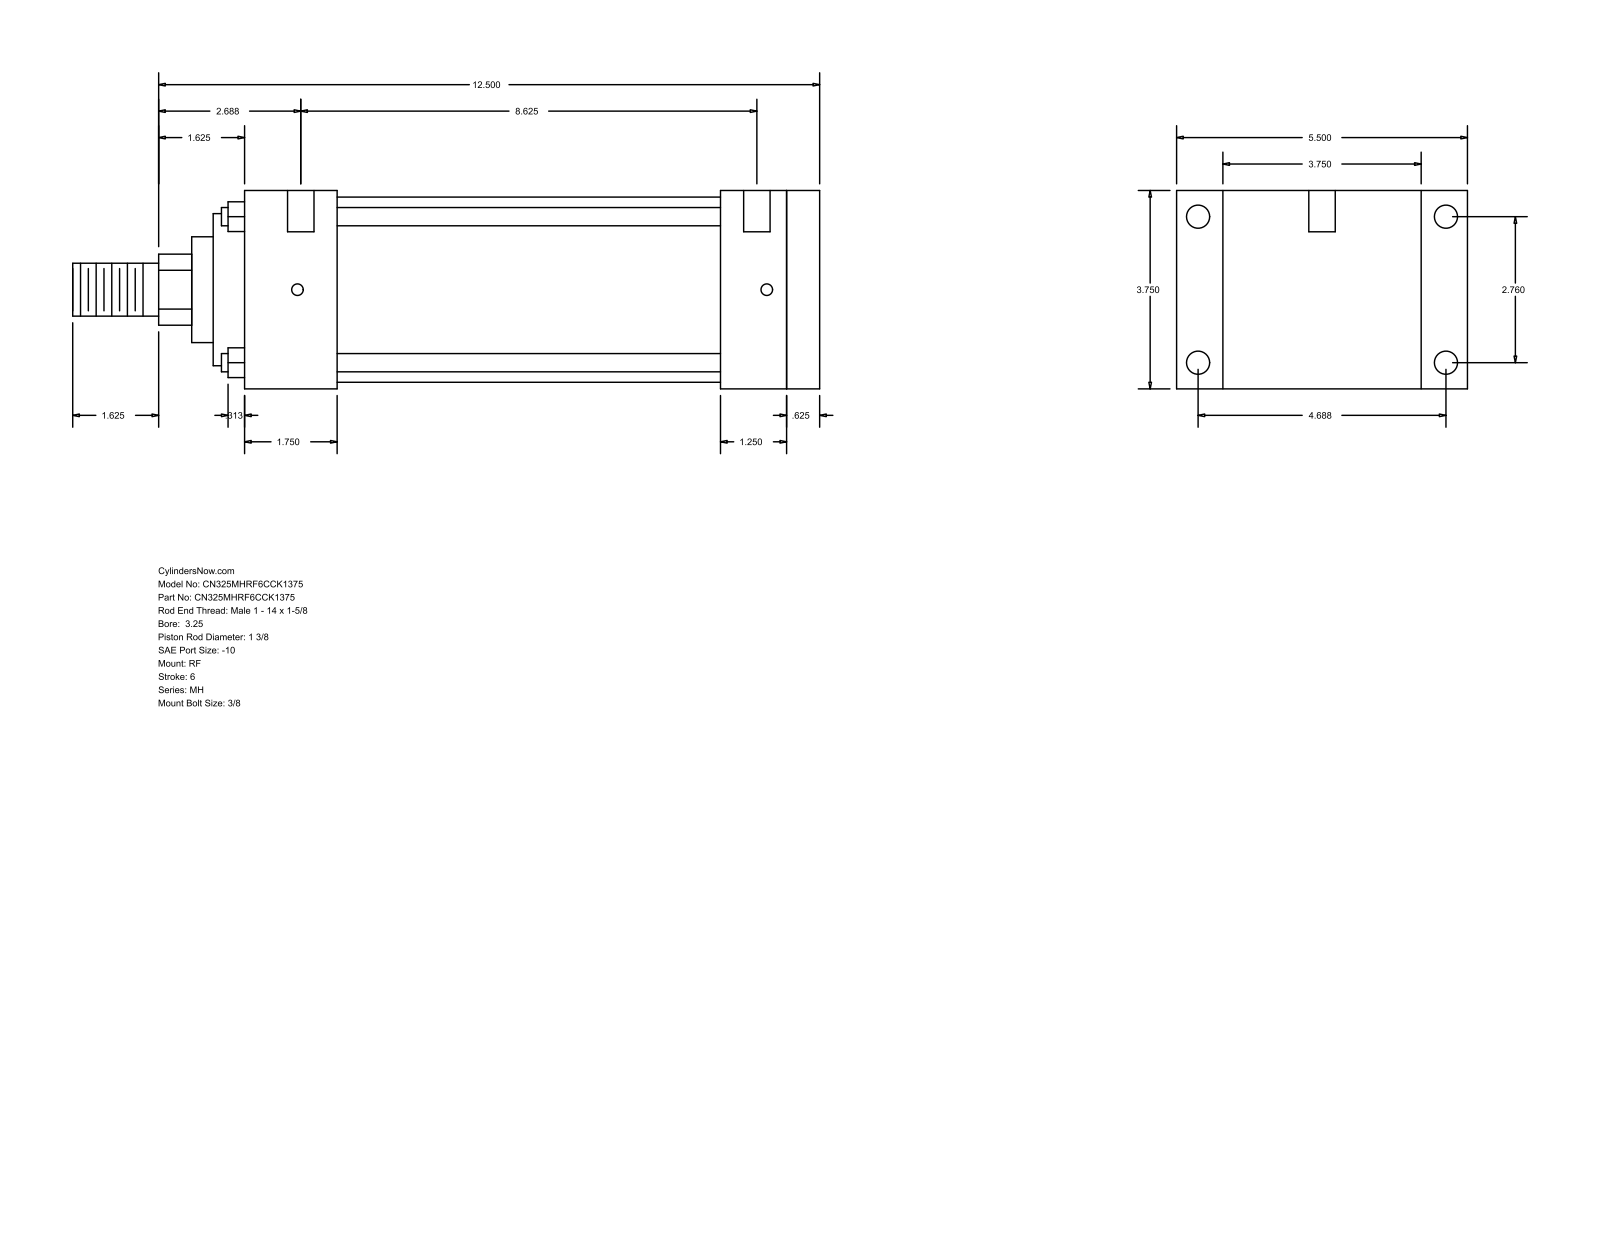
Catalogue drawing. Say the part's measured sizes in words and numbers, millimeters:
The part is named "MH_RF__0325_1.375". Its 3-D file was written by "GSSL Pune (CONFIG_CONTROL_DESIGN)". It is 0 solids with 94 faces: 65 planar, 29 cylindrical and 0 other. Overall it measures 358.77 by 139.7 by 95.25 millimeters. Round holes: 4 of diameter 5.56, 4 of diameter 11.13, 2 of diameter 12.7. Round bosses or shafts: 4 of diameter 8.76, 1 of diameter 88.9, 1 of diameter 73.03, 1 of diameter 50.8, 1 of diameter 34.92, 1 of diameter 25.4. Partial cylindrical surfaces (rounded edges, fillets, slot ends): 1 of radius 17.06. The main face-to-face distances are 95.24, 276.23, 15.88, 260.35, 22.23, 117.47, 44.45, 215.9, 231.78, 228.61. The hole center spacings are 70.1, 119.06, 138.16, 225.43, 1.59, 4.76, 219.08, 220.67.
